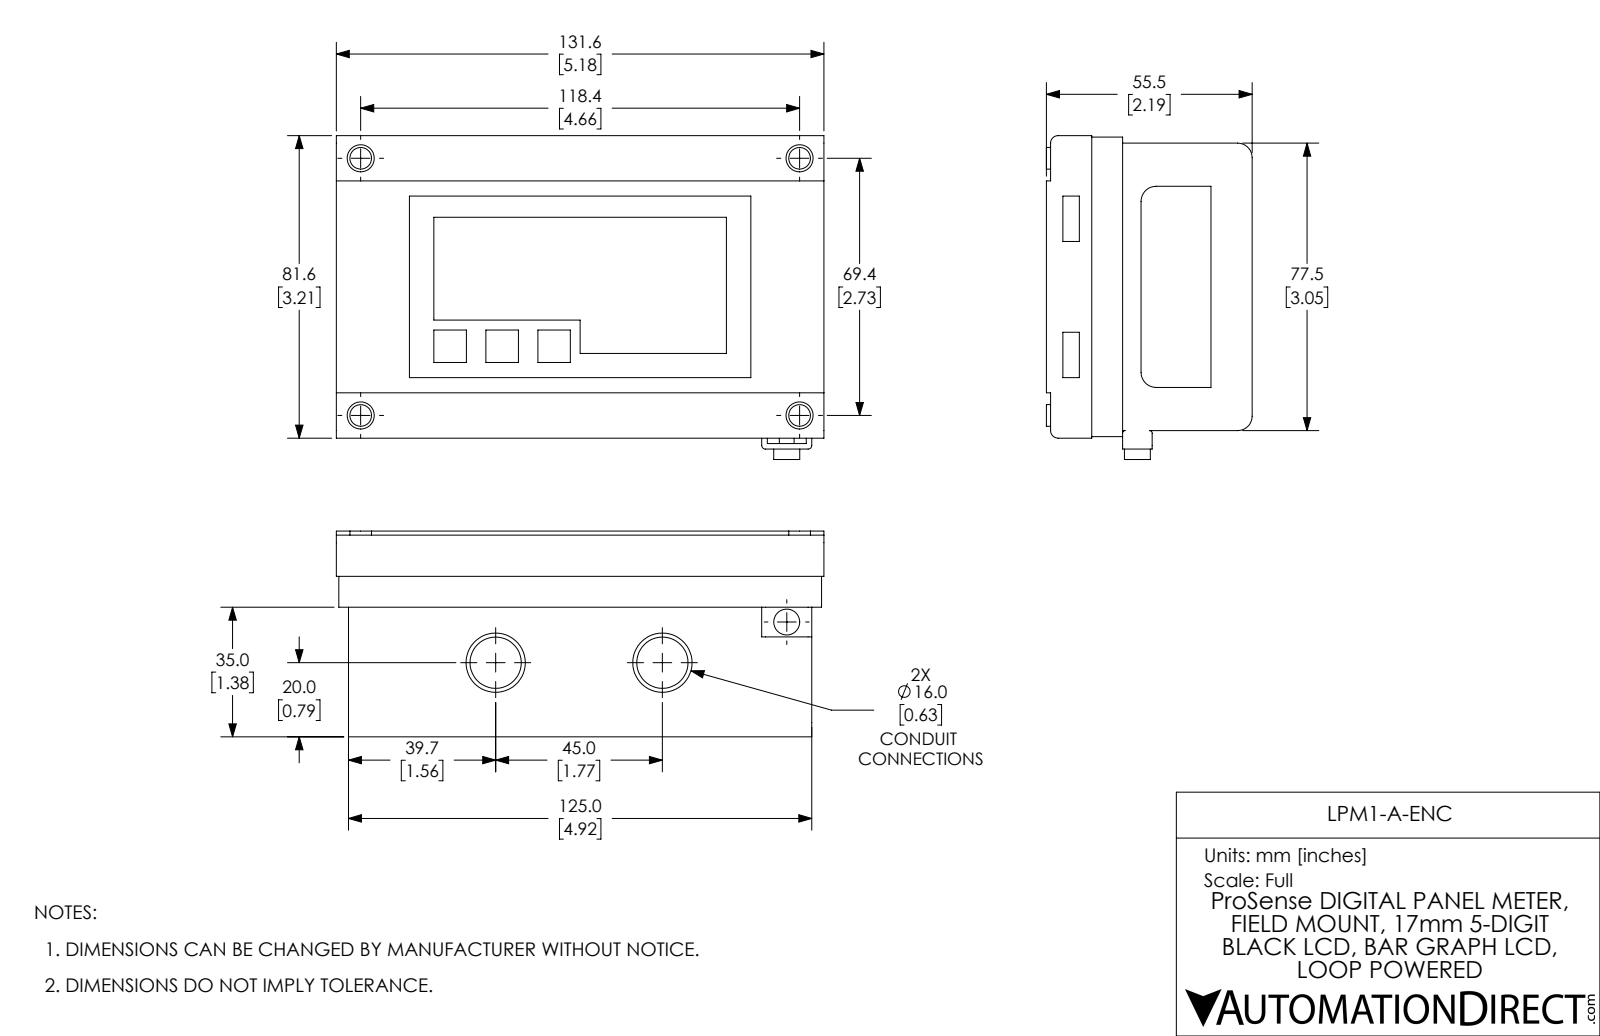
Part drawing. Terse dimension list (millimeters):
name: LPM1-A-ENC
written by: SolidWorks 2017 (AUTOMOTIVE_DESIGN)
unit: mm
bodies: 1 solid, 148 faces (100 planar, 40 cylindrical, 8 other)
size: 131.6 × 87.4 × 55.5
volume: 526 700 mm³; area: 49 330 mm²
holes: 4× ⌀7.3, 2× ⌀13.8, 1× ⌀4.2
bosses: 4× ⌀5.8, 1× ⌀7, 1× ⌀4
rounds: 2× R0.7, 2× R1, 2× R2, 2× R3.9, 2× R4.1
face distances: 77.5, 4.4, 55.5, 3.3, 51.1, 54.4, 1.1, 2, 79.6, 0.4
hole spacings: 69.4, 118.4, 137.3, 35.3, 45, 79.3
